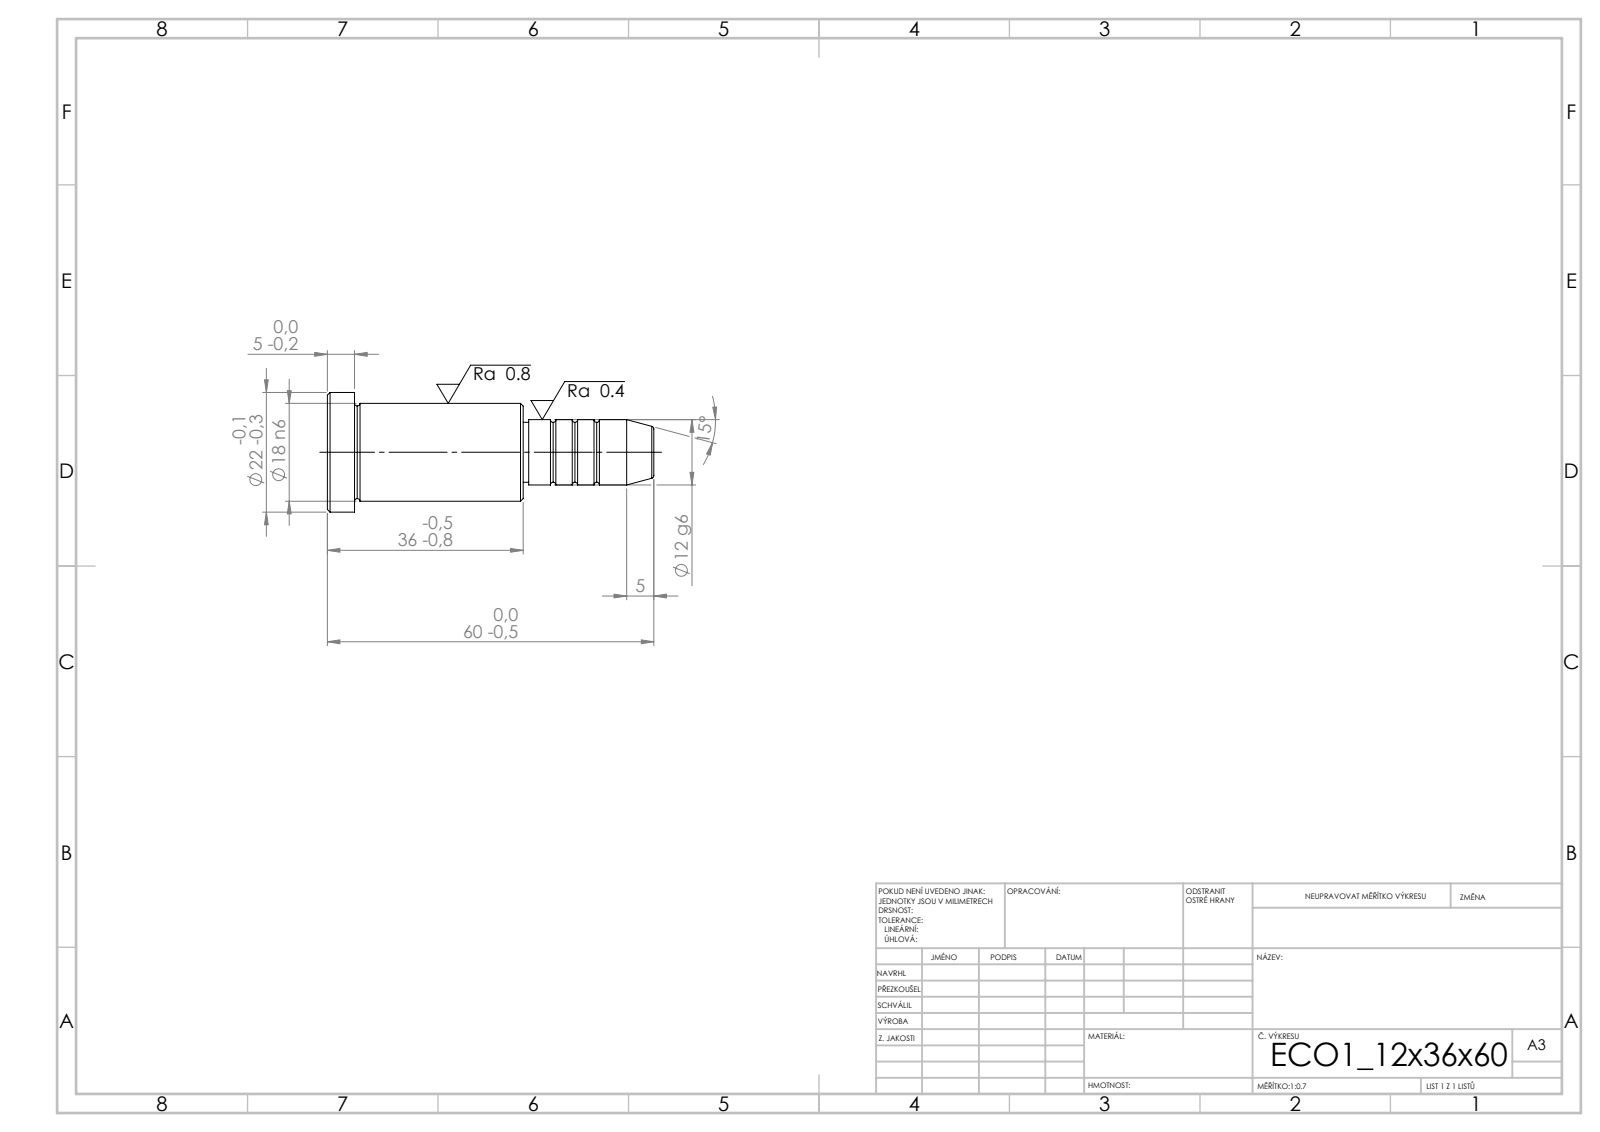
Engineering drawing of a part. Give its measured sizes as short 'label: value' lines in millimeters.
written by: SolidWorks 2019 (CONFIG_CONTROL_DESIGN)
unit: mm
bodies: 1 solid, 43 faces (5 planar, 14 cylindrical, 24 other)
size: 60 × 22 × 22
volume: 12 288 mm³; area: 3 780 mm²
bosses: 1× ⌀22, 1× ⌀18, 1× ⌀12, 1× ⌀11
face distances: 36, 31, 5, 24, 55, 60, 23, 1, 32, 37
